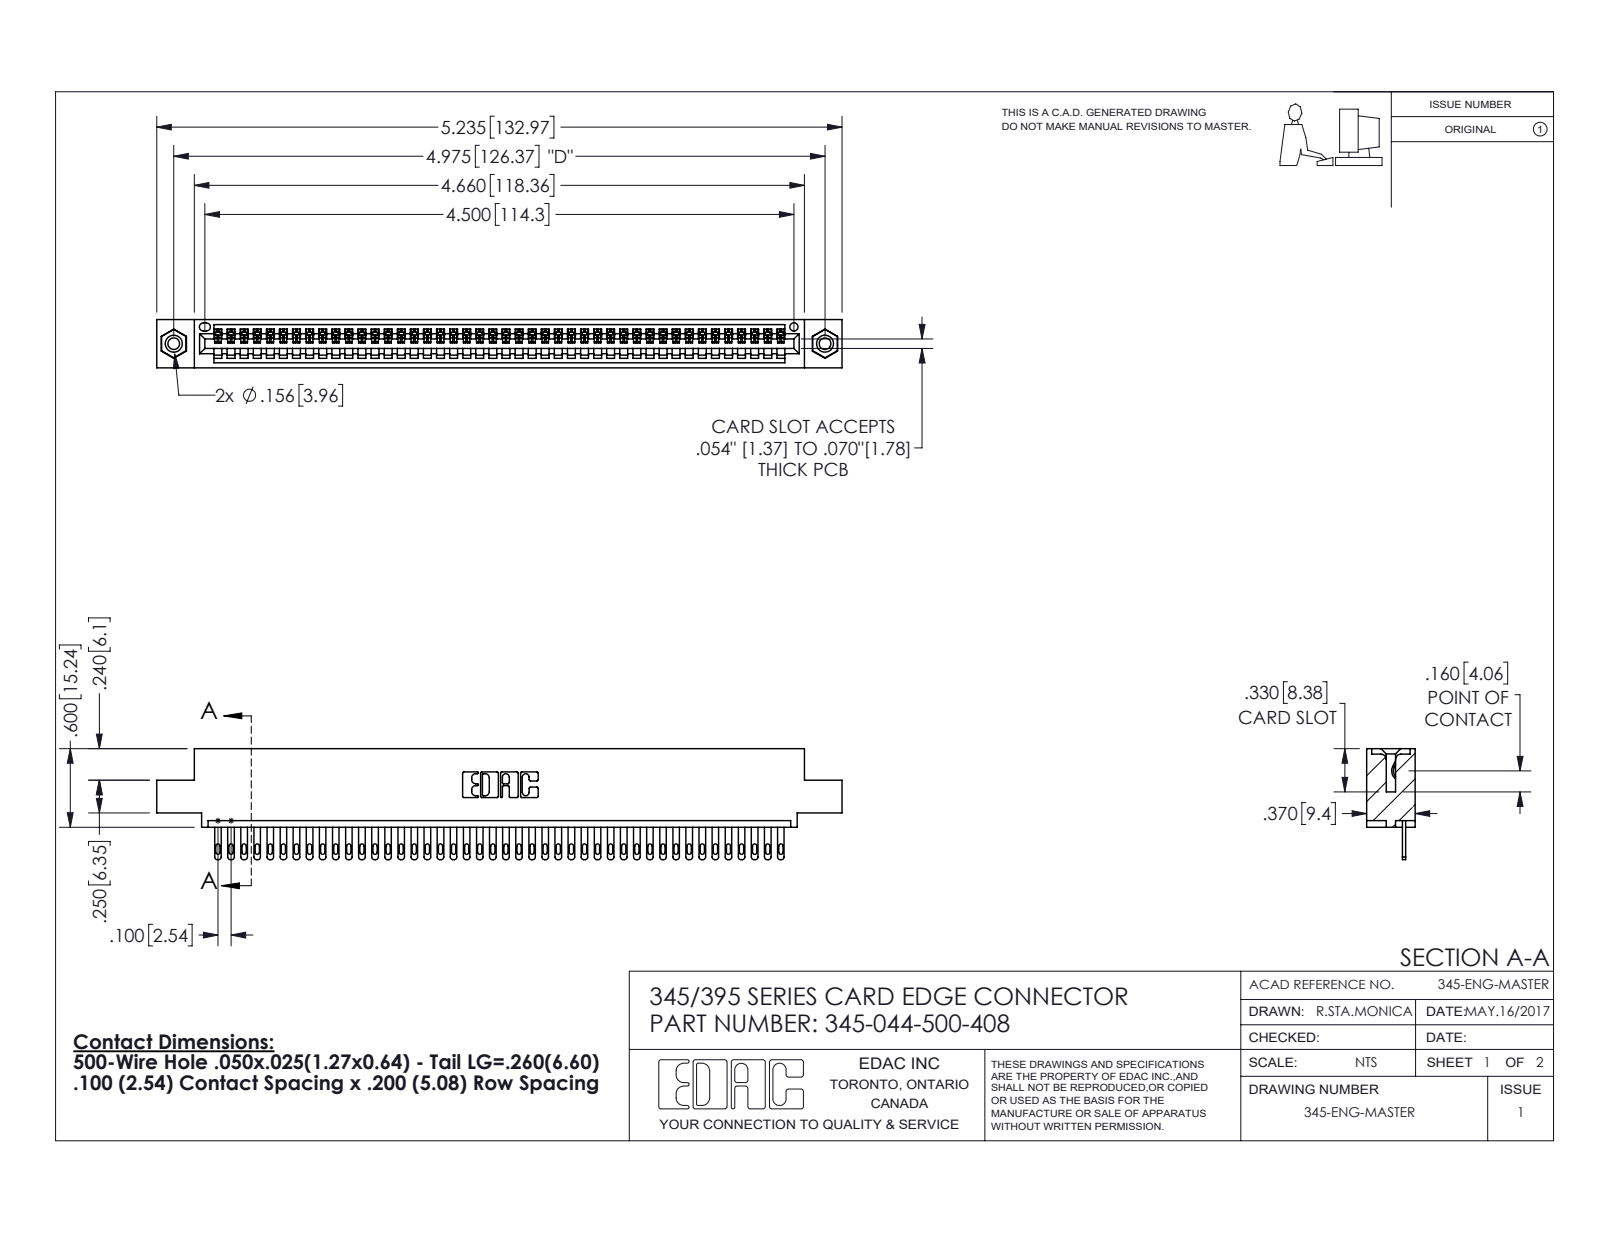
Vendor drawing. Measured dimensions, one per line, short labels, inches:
name: 345-292-001_345-293-100; 345-044-500-408; 345-250-001_345-250-003-102; 345 Part_0.110 Offset - 0.156 Dia-TI
written by: SolidWorks 2016 (CONFIG_CONTROL_DESIGN)
unit: in
bodies: 47 solids, 2566 faces (1612 planar, 938 cylindrical, 16 other)
size: 5.235 × 0.847 × 0.37
volume: 0.768 in³; area: 26.29 in²
holes: 2× ⌀0.089, 2× ⌀0.125, 2× ⌀0.156, 1× ⌀0.064
bosses: 2× ⌀0.155
rounds: 88× R0.006, 88× R0.016, 88× R0.02, 22× R0.01, 6× R0.007, 6× R0.031, 3× R0.026, 2× R0.031
face distances: 0.072, 0.298, 0.37, 0.098, 0.272, 0.025, 0.2, 0.225, 0.149, 0.072
hole spacings: 0.27, 4.739, 4.975
